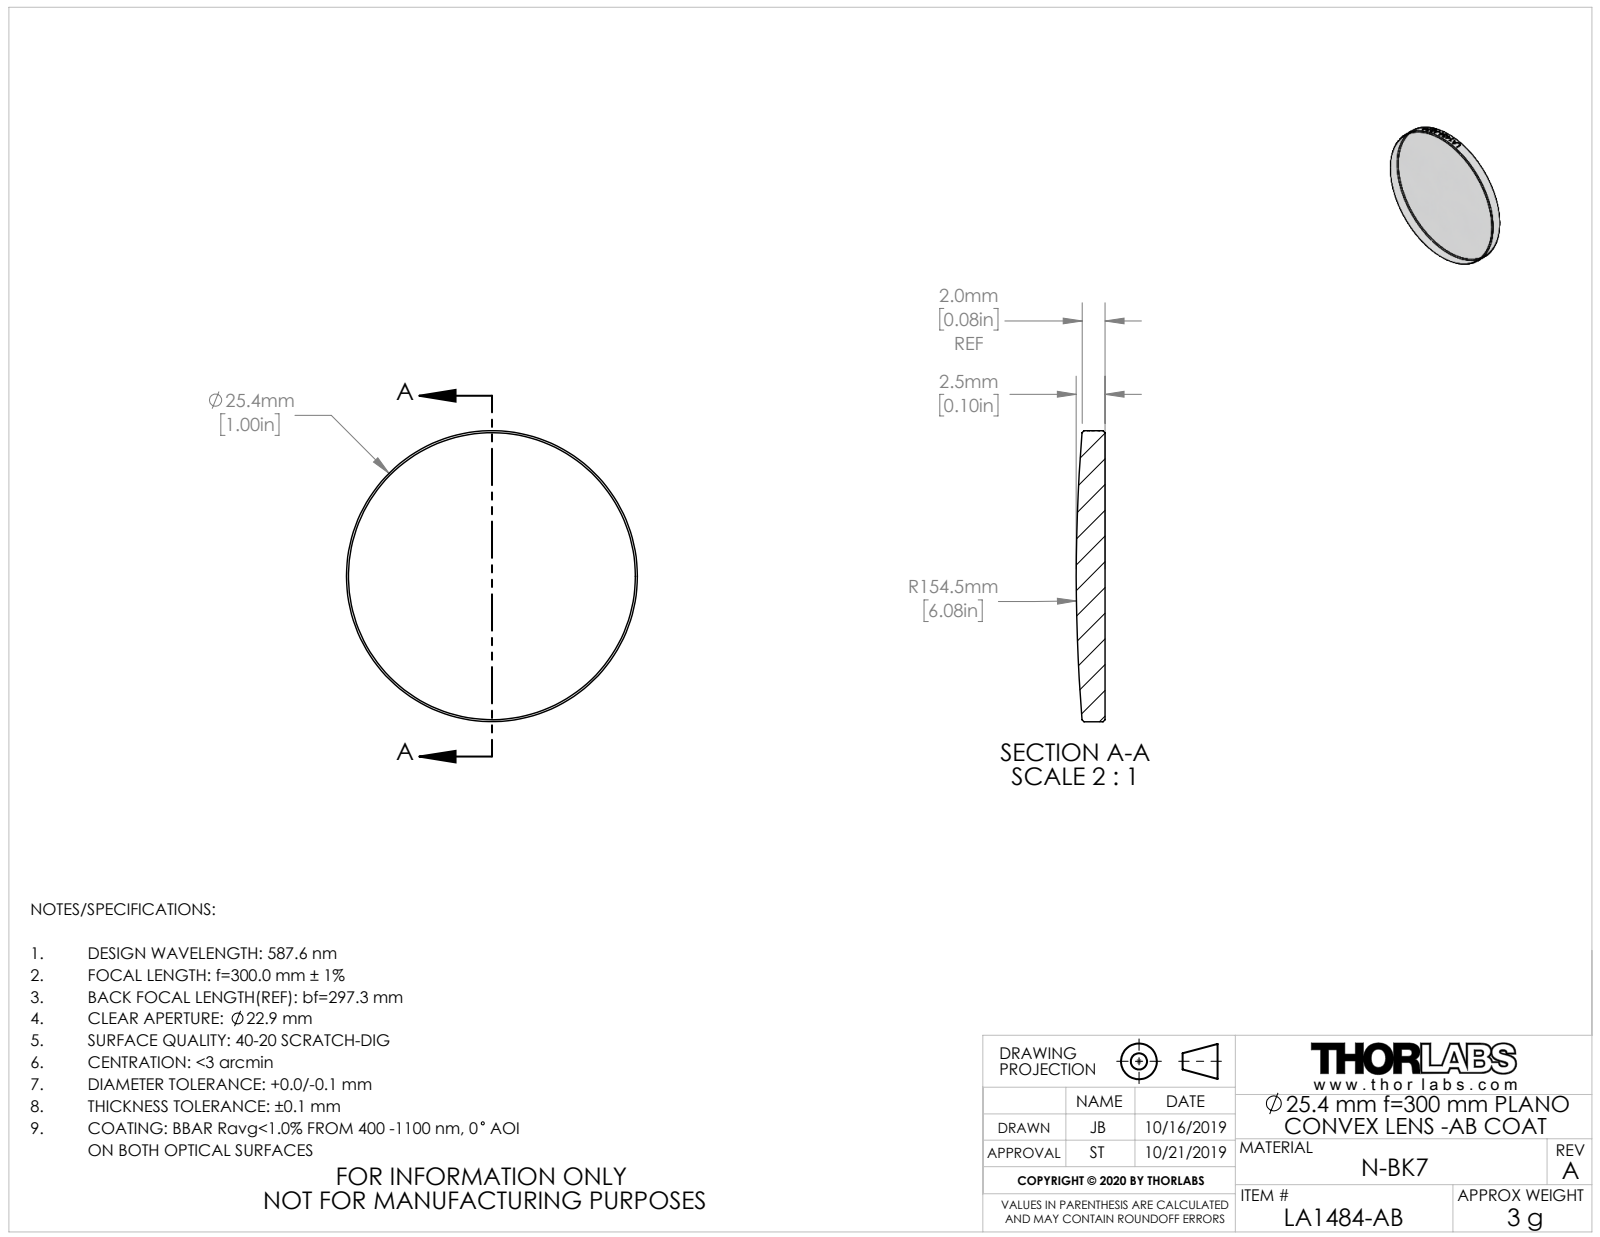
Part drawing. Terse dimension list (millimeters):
name: TTN195781-E0W
written by: SolidWorks 2018 (CONFIG_CONTROL_DESIGN)
unit: mm
bodies: 1 solid, 30 faces (1 planar, 23 cylindrical, 6 other)
size: 25.4 × 25.4 × 2.5
volume: 1 100 mm³; area: 1 158 mm²
bosses: 1× ⌀25.4
